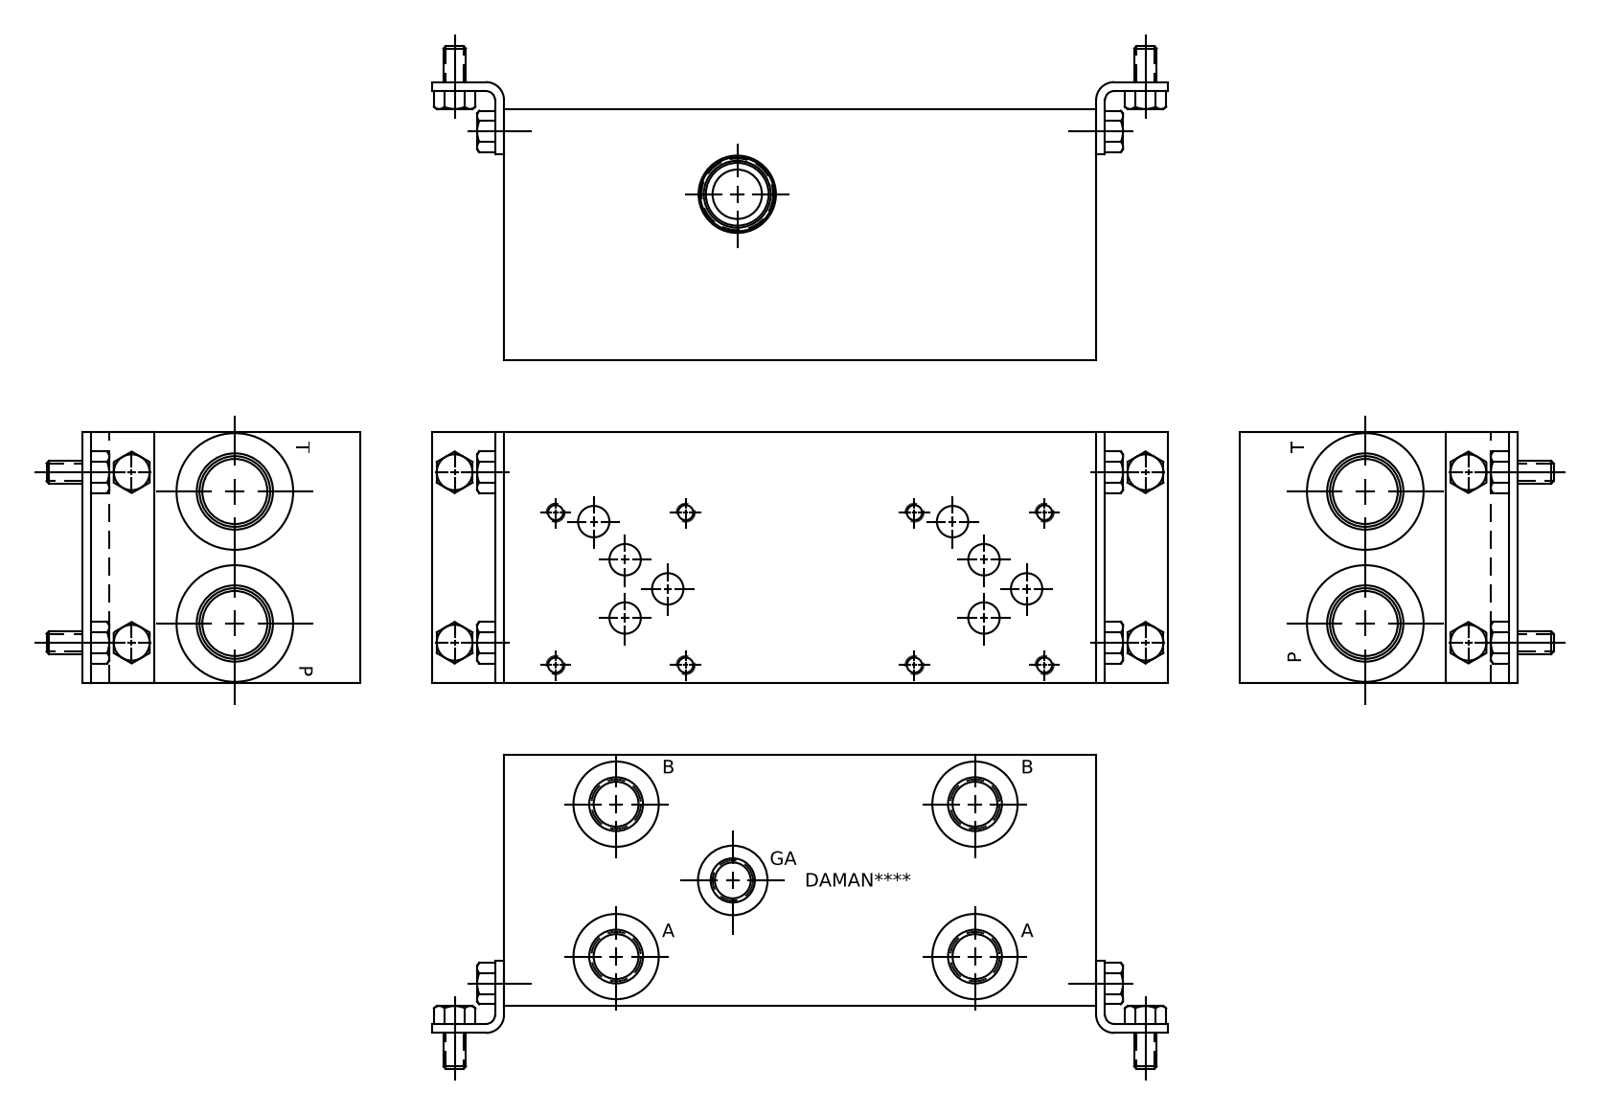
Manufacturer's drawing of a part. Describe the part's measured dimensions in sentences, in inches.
The part is named "D05P025S_S". Its 3-D file was written by "Autodesk Inventor 2021 (AUTOMOTIVE_DESIGN)". It is 1 solid with 675 faces: 358 planar, 83 cylindrical and 234 other. Overall it measures 8.25 by 3.5 by 3.5 inches. Its volume is 92.63 cubic inches and its surface area 180.9 square inches. Round holes: 8 of diameter 0.201, 8 of diameter 0.25, 8 of diameter 0.438, 4 of diameter 0.625, 4 of diameter 0.689, 4 of diameter 0.75, 4 of diameter 0.758, 4 of diameter 1.206, 2 of diameter 0.257, 2 of diameter 0.312, 2 of diameter 0.906, 2 of diameter 0.981. The main face-to-face distances are 3.5, 8.25, 0.031, 8.219, 3.469, 8.188, 0.75, 0.781, 7.469, 7.438. The hole center spacings are 5, 1.813, 2.793, 1.171, 2.125, 5.433, 0.546, 0.719.
